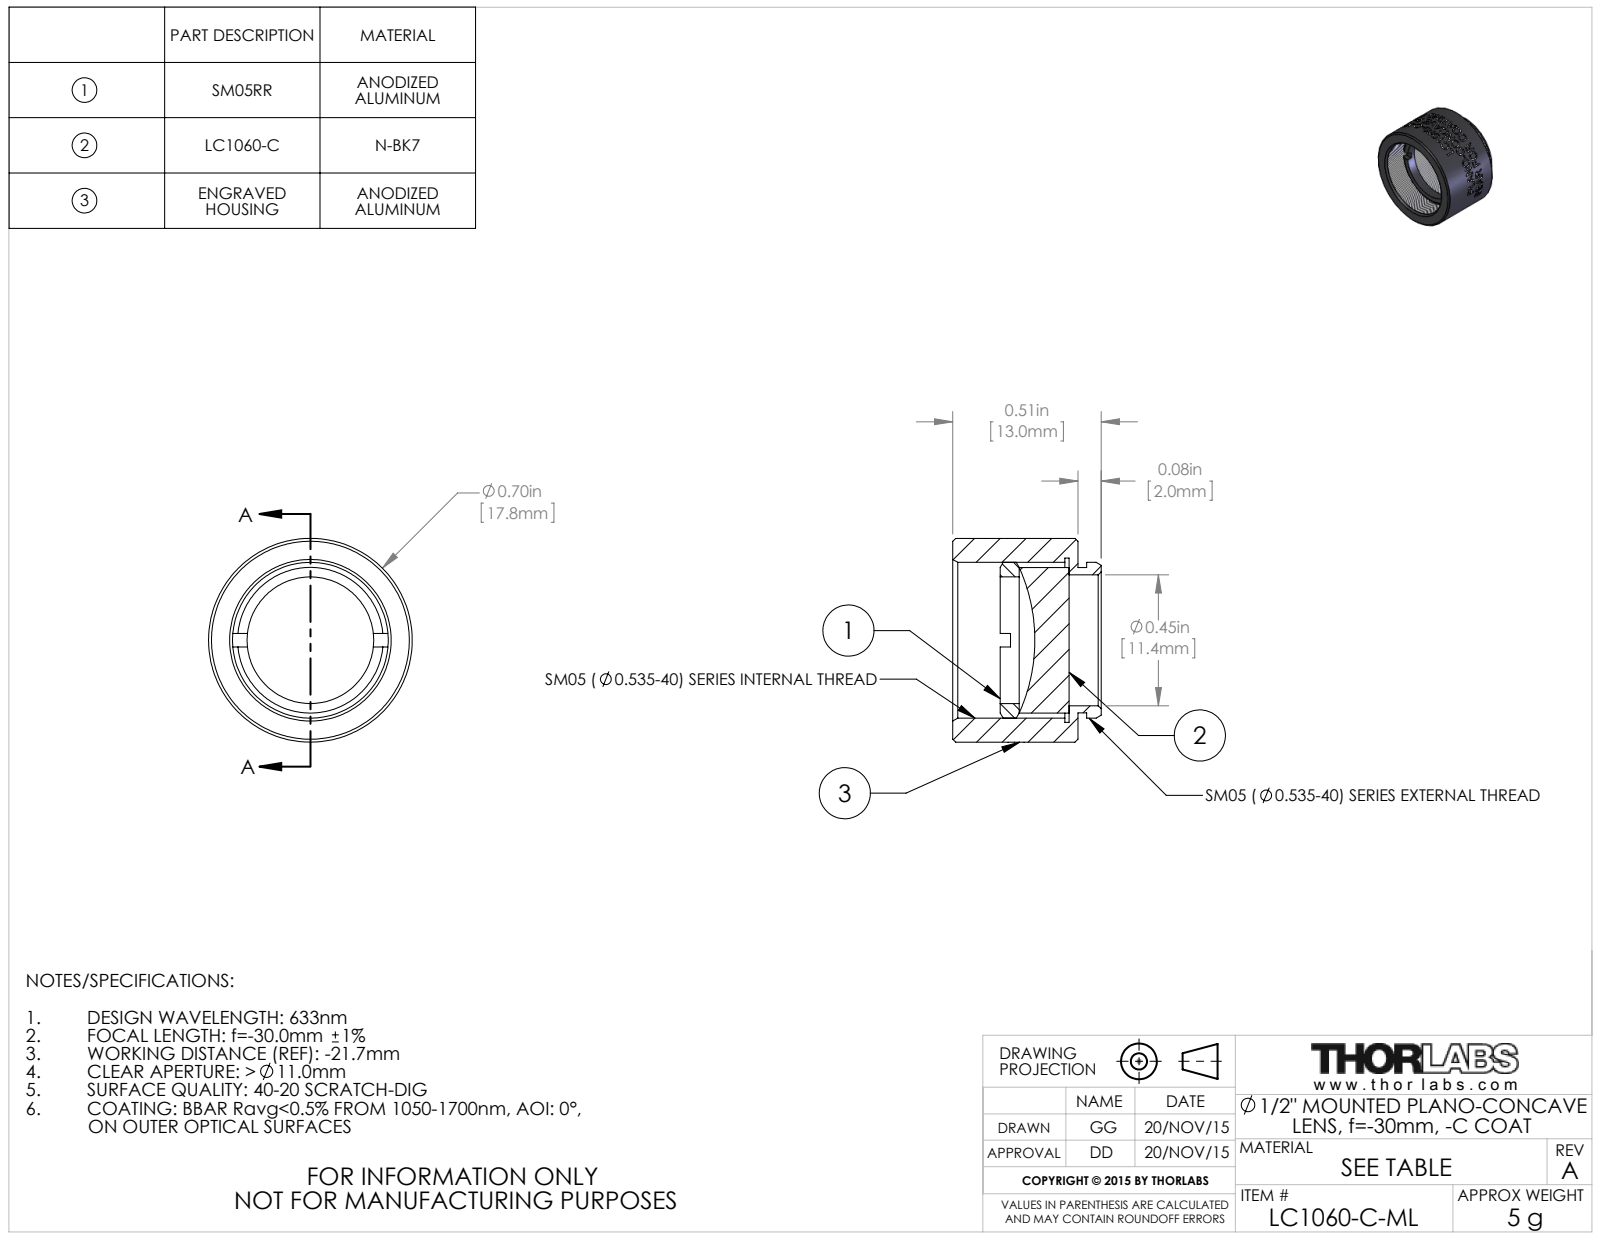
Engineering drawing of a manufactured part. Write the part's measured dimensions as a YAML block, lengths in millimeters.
part_name: "TTN045254-E0W"
step_written_by: "SolidWorks 2014 (CONFIG_CONTROL_DESIGN)"
units: millimeters
bodies: {solids: 3, faces: 151, planar: 16, cylindrical: 118, other: 17}
overall_size: [17.8, 17.8, 13]
volume: 1750
surface_area: 2198
round_holes:
  - {diameter: 11, count: 1}
  - {diameter: 11.4, count: 1}
  - {diameter: 13.6, count: 1}
  - {diameter: 14.4, count: 1}
round_bosses_or_shafts:
  - {diameter: 17.8, count: 1}
  - {diameter: 13.6, count: 1}
  - {diameter: 12.7, count: 1}
  - {diameter: 12.7, count: 1}
face_to_face_distances: [0.8, 10.9, 10.2, 5.1, 4.4, 5.8, 6.8, 6, 1.7, 4.1]
